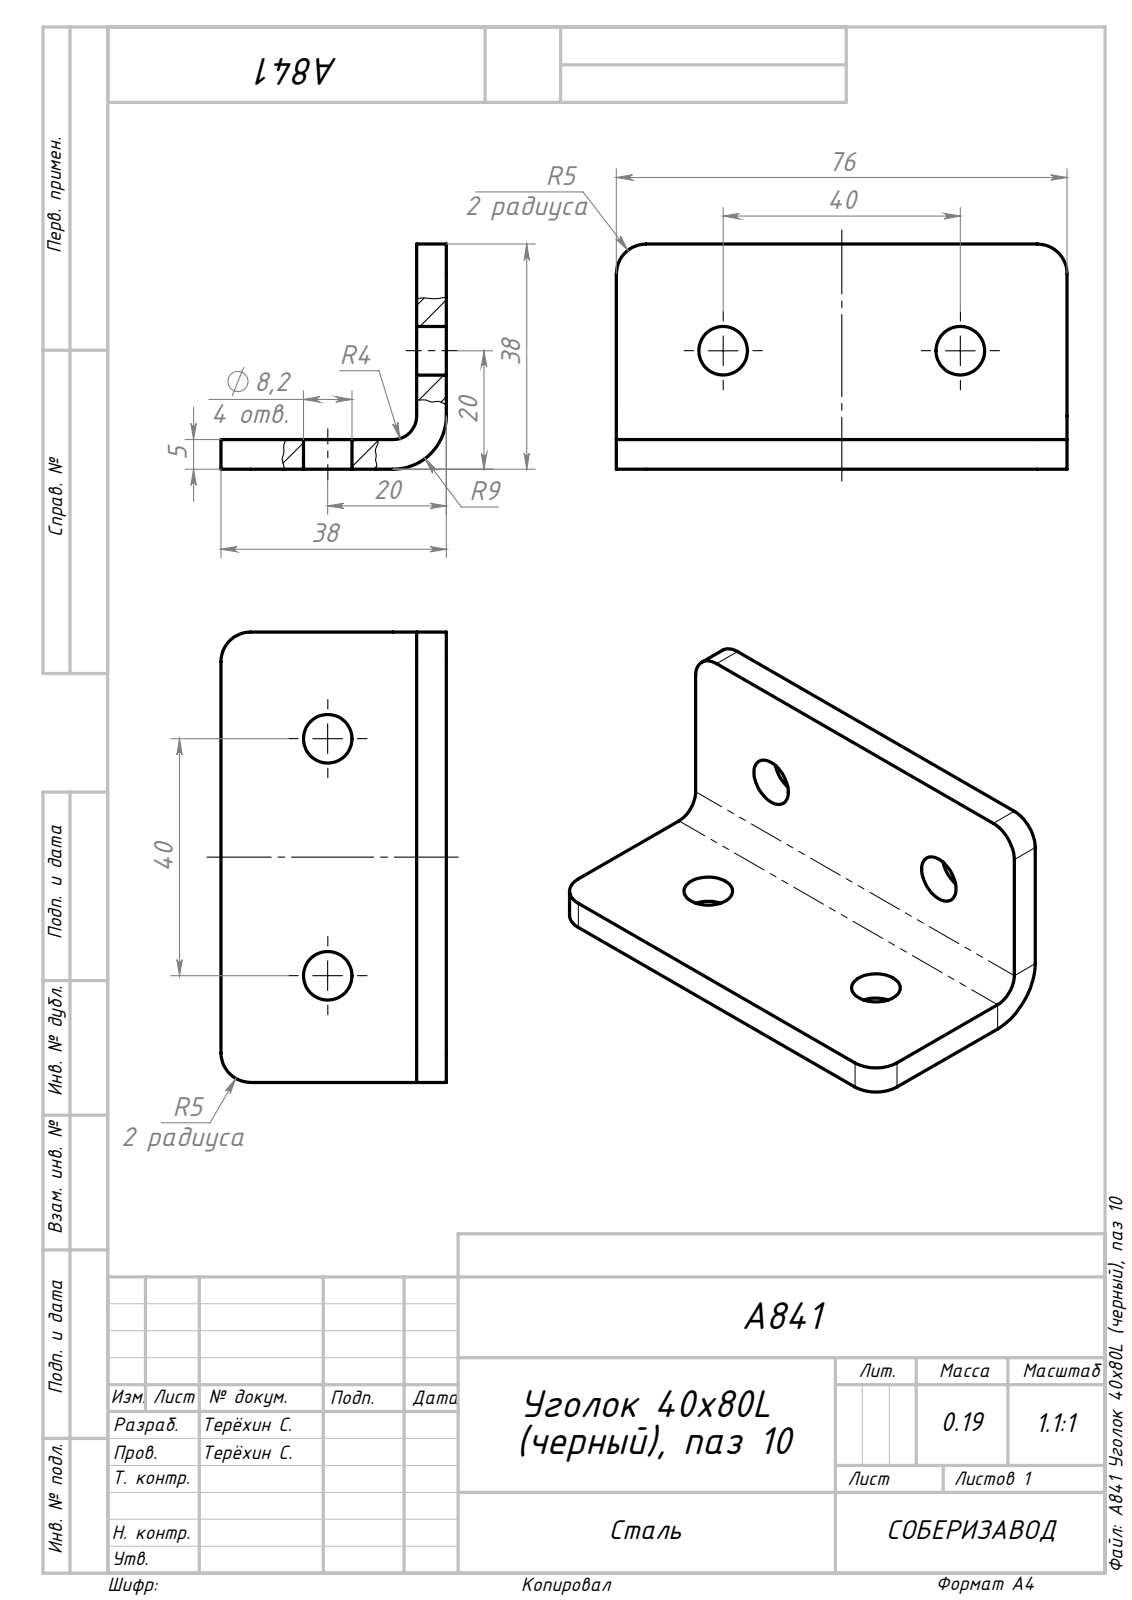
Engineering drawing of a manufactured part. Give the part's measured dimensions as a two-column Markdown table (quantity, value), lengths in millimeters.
| quantity | value |
| --- | --- |
| part name | A841 Уголок 40х80L (черный), паз 10_00; Сборка4 |
| STEP written by | SolidWorks 2022 (AUTOMOTIVE_DESIGN) |
| units | millimeters |
| bodies | 1 solid, 26 faces (12 planar, 14 cylindrical, 0 other) |
| overall size | 76 × 38 × 38 |
| volume | 24 756 mm³ |
| surface area | 11 817 mm² |
| round holes (diameter × count) | 8.2 × 4 |
| partial cylindrical surfaces (radius × count) | 5 × 4, 4 × 1, 9 × 1 |
| main face-to-face distances | 5, 38, 33, 76 |
| hole center spacings | 40 |
